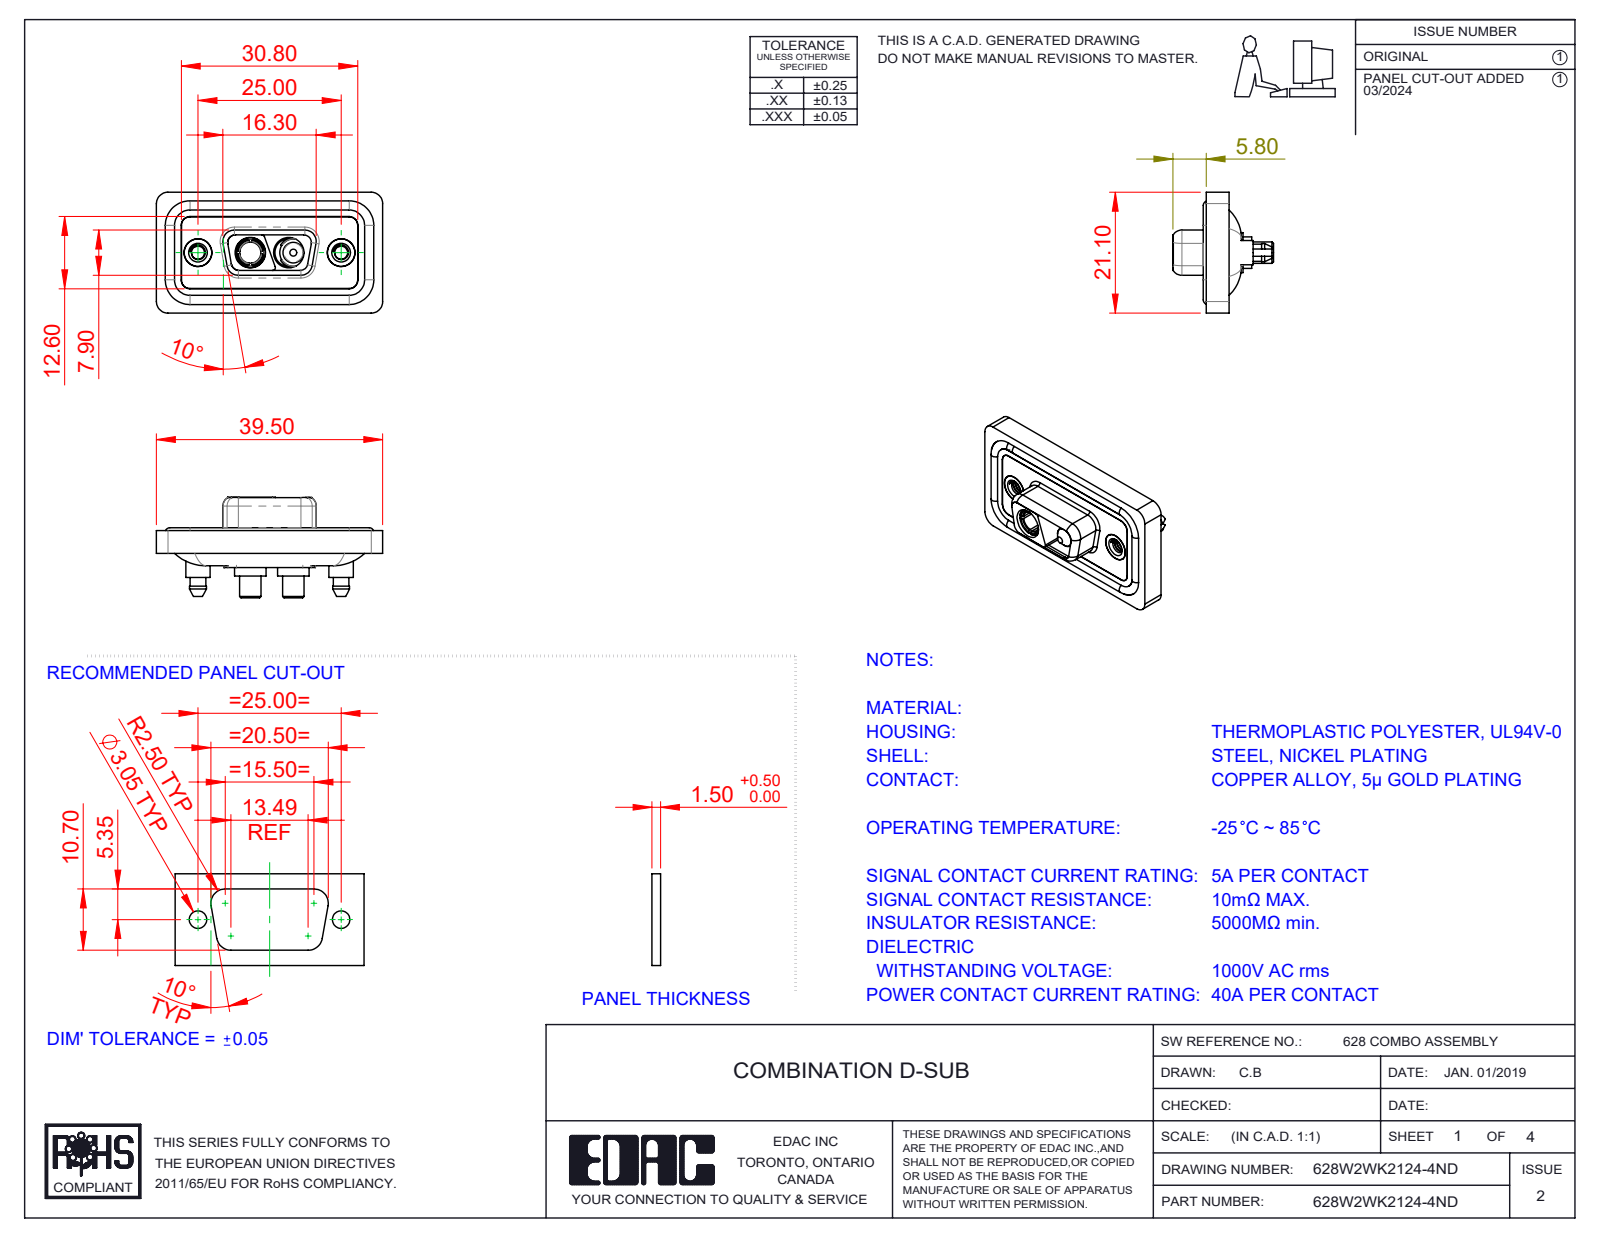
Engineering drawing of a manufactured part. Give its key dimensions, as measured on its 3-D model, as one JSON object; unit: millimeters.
{"part_name": "628W2WK2124-4ND; 628Combo Threaded Boardlock_D; Power Pin_40A S; 628Combo Shell Rear_09 Contacts (+4 more)", "step_written_by": "SolidWorks 2023 (CONFIG_CONTROL_DESIGN)", "units": "millimeters", "bodies": {"solids": 11, "faces": 566, "planar": 160, "cylindrical": 279, "other": 127}, "overall_size": [39.5, 21.1, 17.55], "volume_mm3": 4775, "surface_area_mm2": 7705, "round_holes": [[4.85, 4], [2.26, 2], [4, 2], [4.05, 2], [5, 2], [5.3, 2], [3.7, 1]], "round_bosses_or_shafts": [[1.6, 4], [5.5, 2], [5.4, 2], [5.2, 2], [4.95, 2], [4.8, 2], [4.75, 2], [4.25, 2]], "partial_cylinders_radius": [[1.5, 24], [2, 18], [1.6, 10], [1.35, 8], [0.5, 6], [0.25, 4], [0.6, 4], [0.65, 4]], "face_to_face_distances": [0.4, 1.1, 2.9, 1.6, 0.5, 1.8, 5.65, 4, 1.5, 5.35], "hole_center_spacings": [9.14, 15.86, 6.72, 25]}
